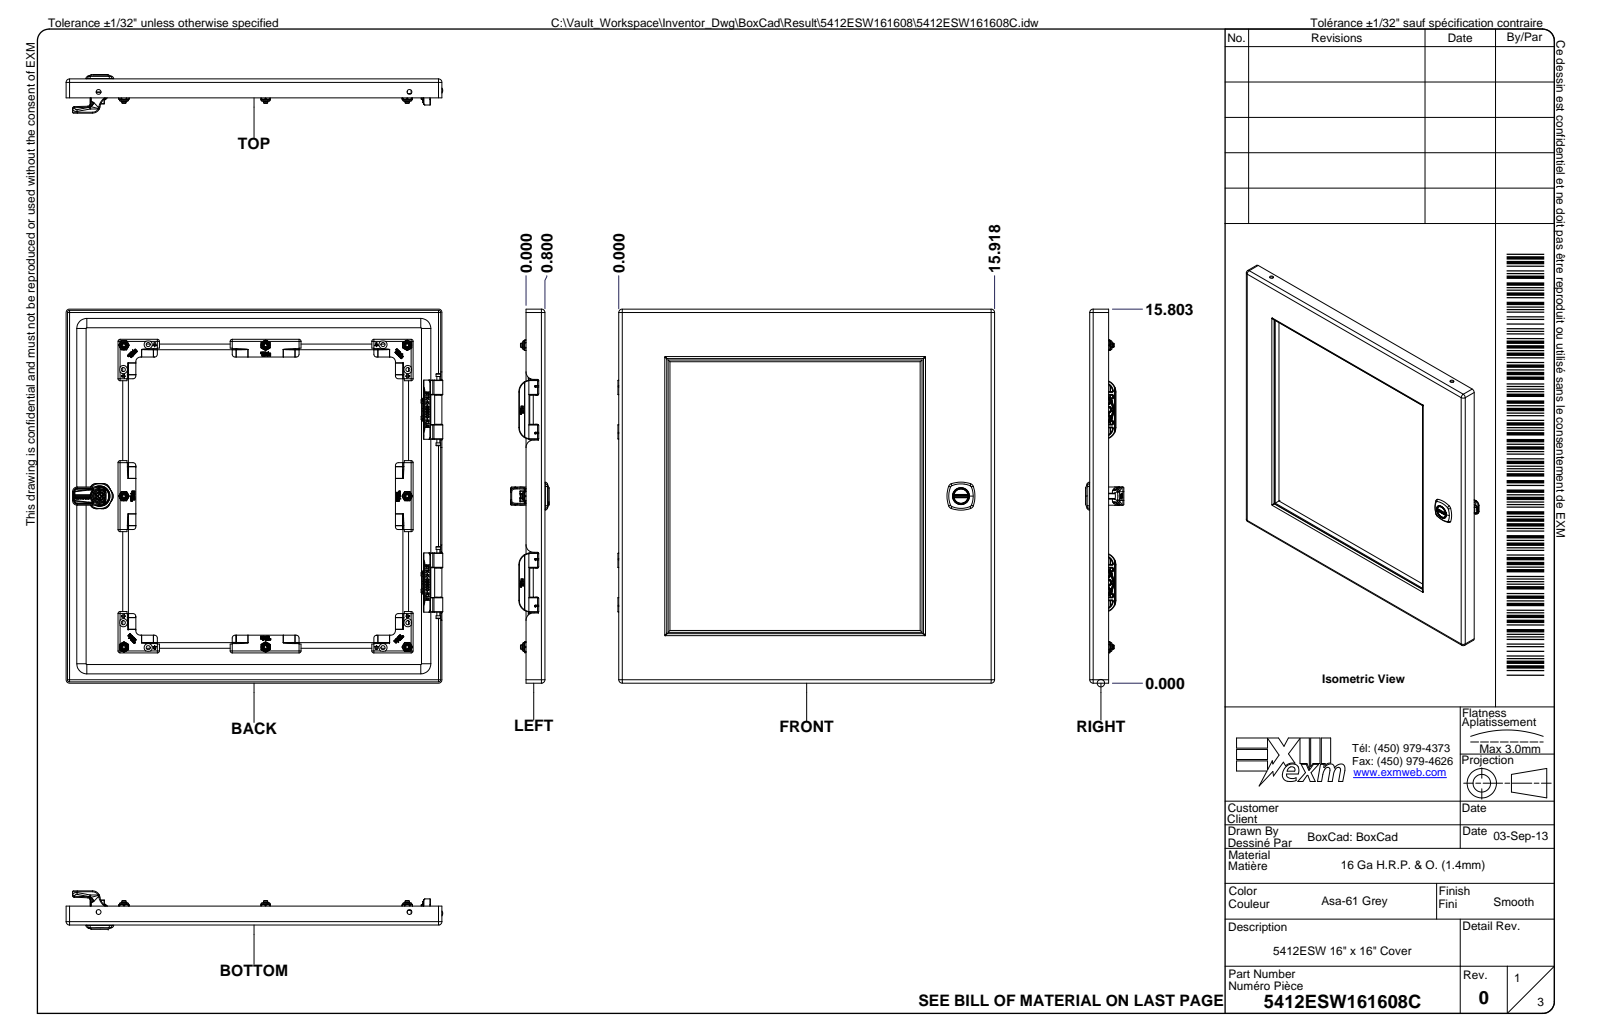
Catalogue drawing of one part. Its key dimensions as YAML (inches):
part_name: "5412ESW161608; 5412ESW161608B; 5412ESW161608B-P; STK-Q-16005 (+8 more)"
step_written_by: "Autodesk Inventor 2024 (AUTOMOTIVE_DESIGN)"
units: inches
bodies: {solids: 77, faces: 11880, planar: 4894, cylindrical: 2749, other: 4237}
overall_size: [16.003, 16, 9.31]
volume: 132.7
surface_area: 3187
round_holes:
  - {diameter: 0.03, count: 13}
  - {diameter: 0.29, count: 12}
  - {diameter: 0.315, count: 12}
  - {diameter: 0.201, count: 11}
  - {diameter: 0.043, count: 8}
  - {diameter: 0.173, count: 8}
  - {diameter: 0.197, count: 8}
  - {diameter: 0.276, count: 8}
  - {diameter: 0.374, count: 8}
  - {diameter: 0.178, count: 4}
  - {diameter: 0.27, count: 4}
  - {diameter: 0.39, count: 4}
round_bosses_or_shafts:
  - {diameter: 0.03, count: 13}
  - {diameter: 0.232, count: 12}
  - {diameter: 0.354, count: 8}
  - {diameter: 0.271, count: 8}
  - {diameter: 0.039, count: 8}
  - {diameter: 0.717, count: 4}
  - {diameter: 0.311, count: 4}
  - {diameter: 0.262, count: 4}
partial_cylinders:
  - {radius: 0.02, count: 245}
  - {radius: 0.039, count: 113}
  - {radius: 0.01, count: 107}
  - {radius: 0.031, count: 82}
  - {radius: 0.008, count: 78}
  - {radius: 0.086, count: 48}
  - {radius: 0.016, count: 46}
  - {radius: 0.084, count: 28}
face_to_face_distances: [0.053, 15.947, 9.081, 15.894, 16, 0.927, 0.874, 1.032, 0.979, 0.105]
hole_center_spacings: [13.422, 1.028, 7.303, 0.35, 0.735, 1.052, 1.385, 1.591]
